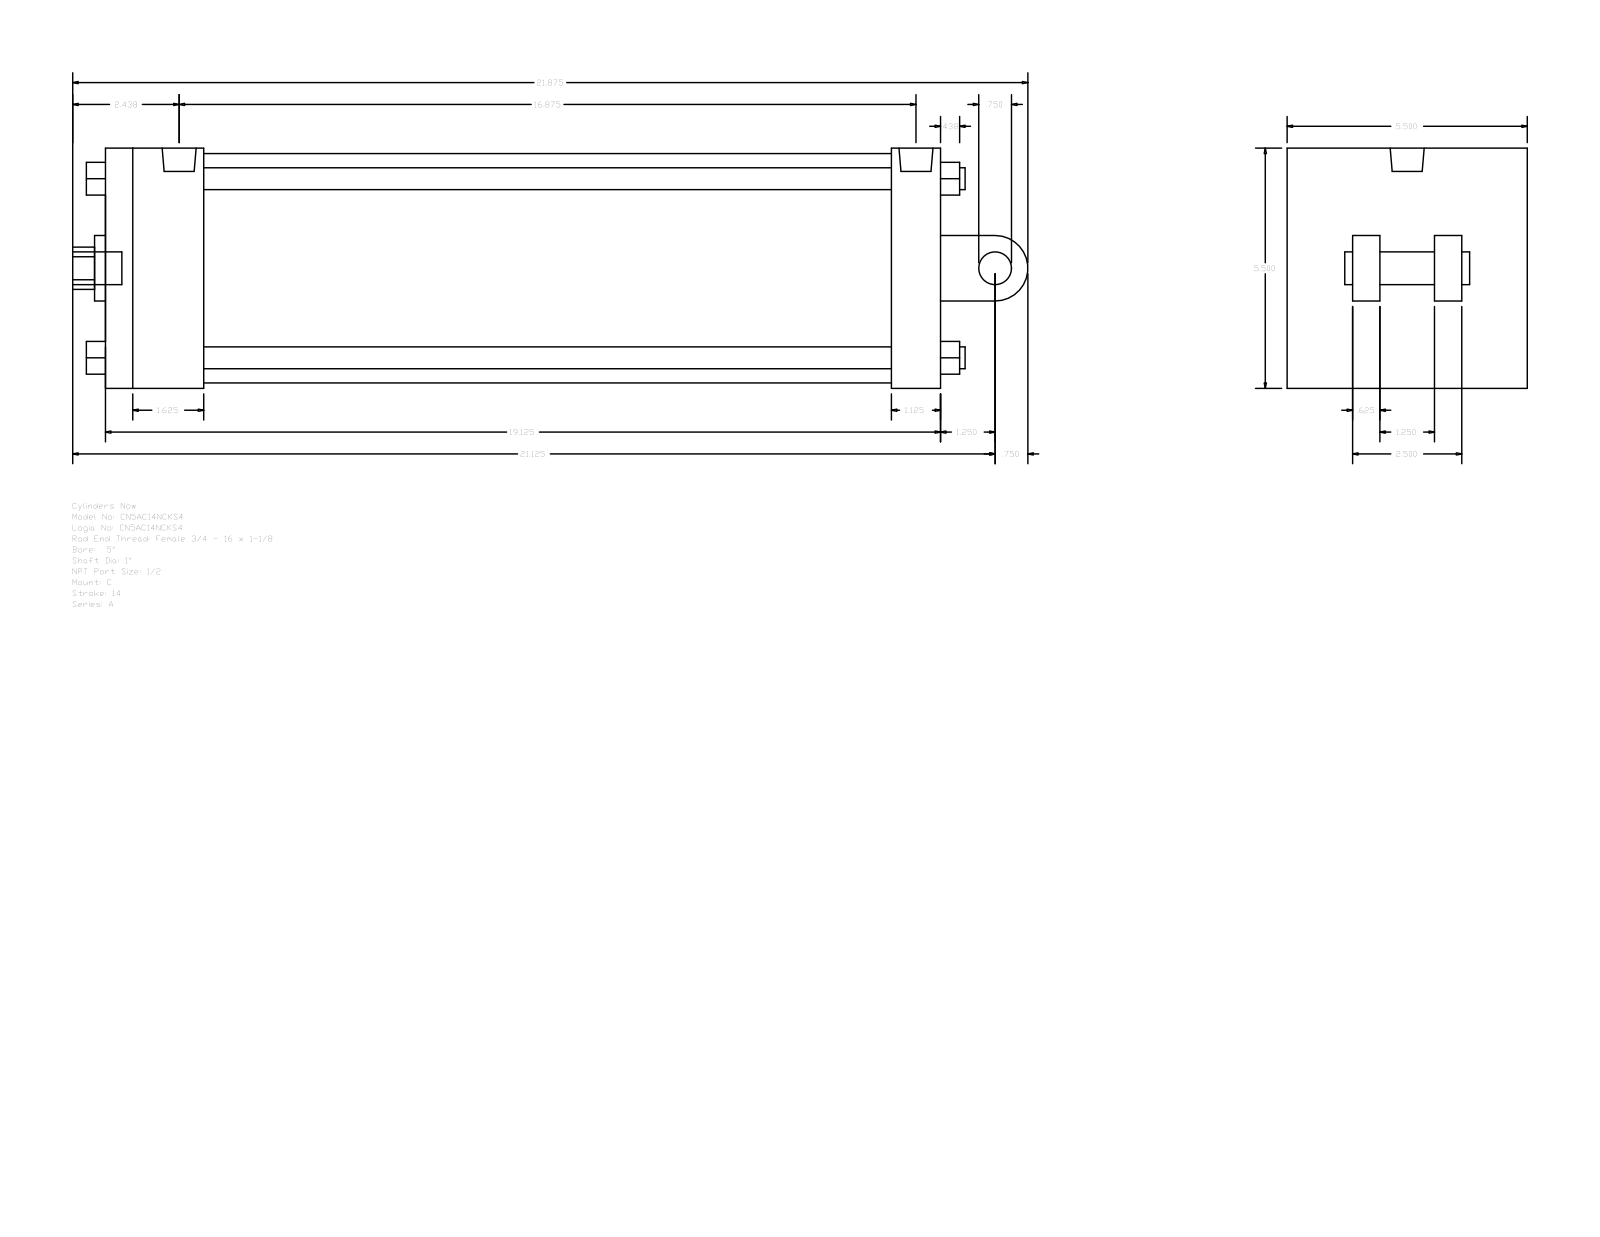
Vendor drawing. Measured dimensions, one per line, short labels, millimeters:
name: A_C__0500_1
written by: GSSL Pune (CONFIG_CONTROL_DESIGN)
unit: mm
bodies: 0 solids, 135 faces (102 planar, 33 cylindrical, 0 other)
size: 555.62 × 139.7 × 139.7
holes: 2× ⌀8.73, 1× ⌀19.77, 1× ⌀25.4, 1× ⌀38.1, 1× ⌀133.35
bosses: 4× ⌀12.7, 2× ⌀19.05, 2× ⌀8.73, 1× ⌀19.77
rounds: 1× R12.29, 1× R19.05
face distances: 139.7, 485.77, 28.57, 57.15, 457.2, 400.05, 428.62, 38.1, 15.87, 47.63
hole spacings: 2.39
